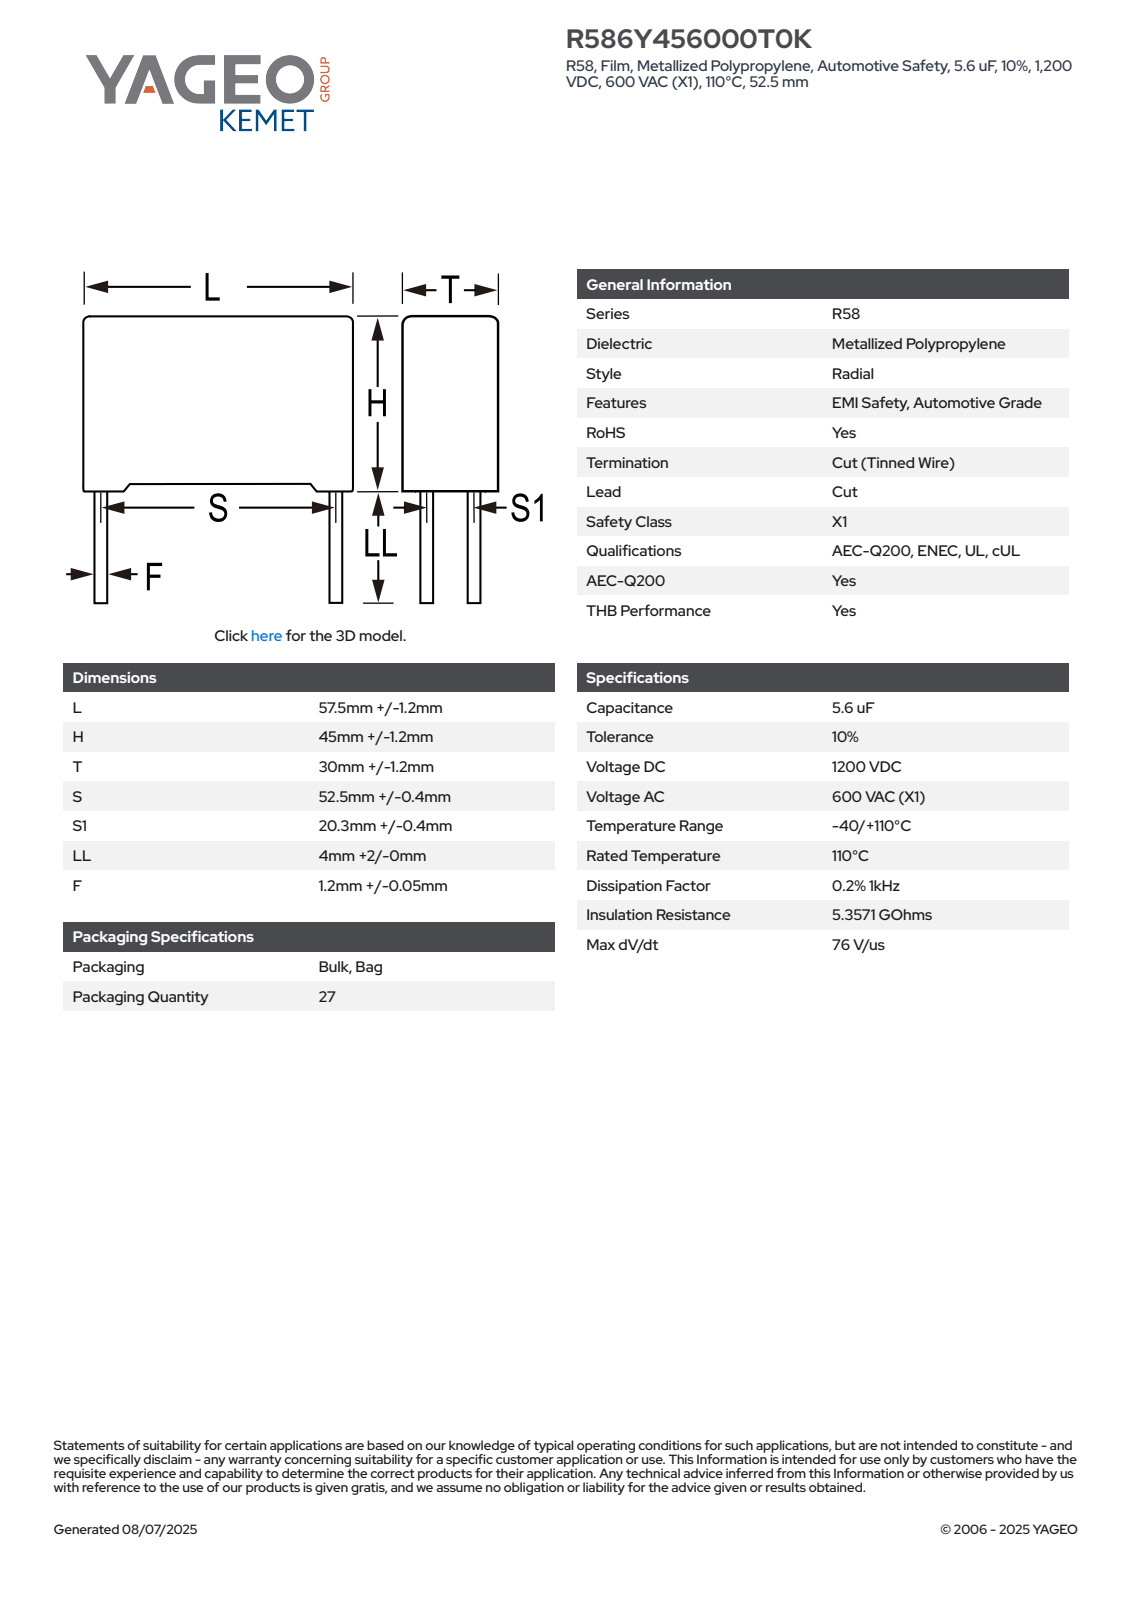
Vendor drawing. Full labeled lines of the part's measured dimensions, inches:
Part name (STEP PRODUCT): CFP_RB4_57.5X45X30_L58.7H46.2T31.2S52.5S120.3LL6F1.25
STEP written by: SolidWorks 2021 (AUTOMOTIVE_DESIGN)
Units: inches
Bodies: 4 solids, 87 faces (79 planar, 8 cylindrical, 0 other)
Overall size (bounding box): 2.311 × 2.055 × 1.228
Volume: 5.028 in³ · Surface area: 19.07 in²
Round bosses / shafts (diameter × count): ⌀0.049 ×4
Main face-to-face distances: 1.228, 1.765, 2.311, 0.054, 1.819, 1.229, 0.076, 2.235, 2.16, 1.153
